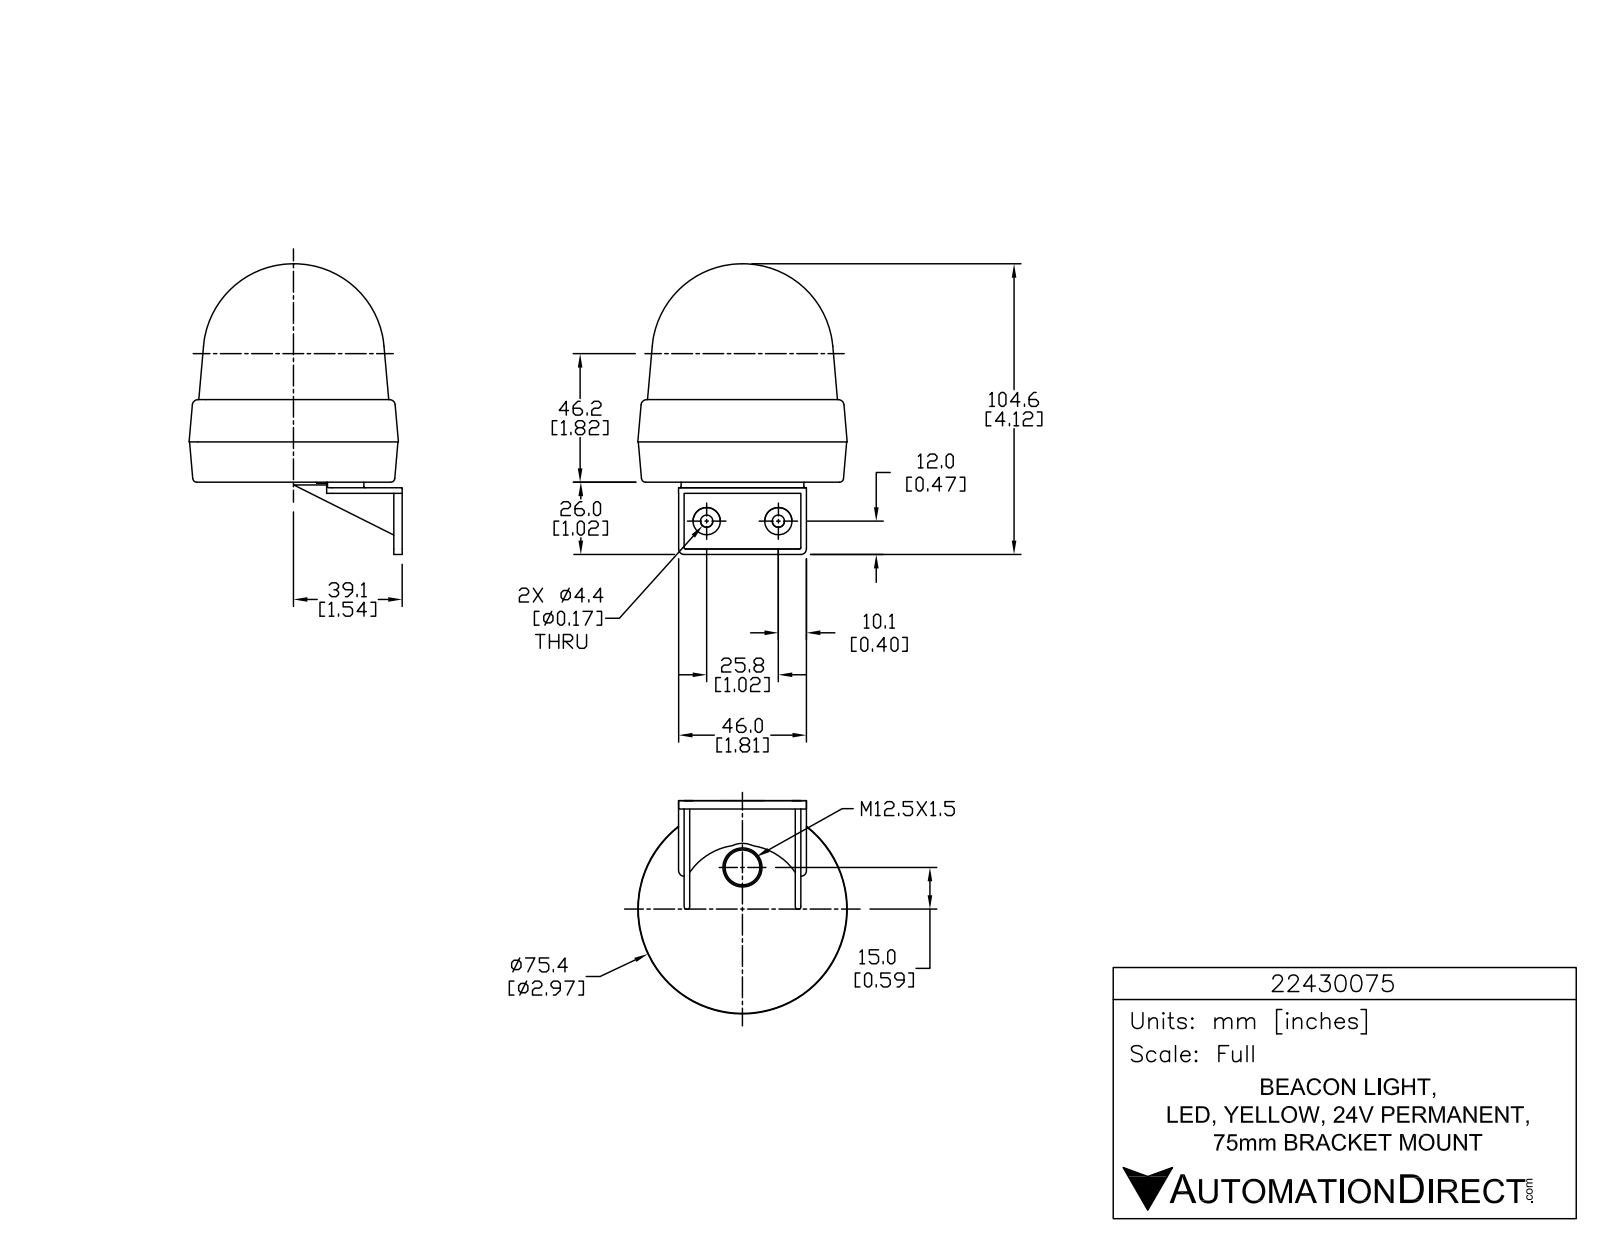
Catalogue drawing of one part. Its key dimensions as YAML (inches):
part_name: "22430075"
step_written_by: "SolidWorks 2015 (AUTOMOTIVE_DESIGN)"
units: inches
bodies: {solids: 1, faces: 819, planar: 549, cylindrical: 180, other: 90}
overall_size: [4.117, 3.253, 2.967]
volume: 16.02
surface_area: 41.97
round_holes:
  - {diameter: 0.059, count: 3}
  - {diameter: 0.173, count: 2}
round_bosses_or_shafts:
  - {diameter: 0.339, count: 3}
  - {diameter: 0.084, count: 3}
  - {diameter: 0.386, count: 2}
partial_cylinders:
  - {radius: 0.005, count: 9}
  - {radius: 0.005, count: 6}
  - {radius: 0.012, count: 6}
  - {radius: 0.012, count: 6}
  - {radius: 0.012, count: 6}
  - {radius: 0.02, count: 6}
  - {radius: 0.196, count: 6}
  - {radius: 0.079, count: 4}
face_to_face_distances: [0.079, 0.157, 1.574, 0.039, 0.118, 1.653, 1.496, 0.079, 1.654, 1.732]
hole_center_spacings: [1.016]
